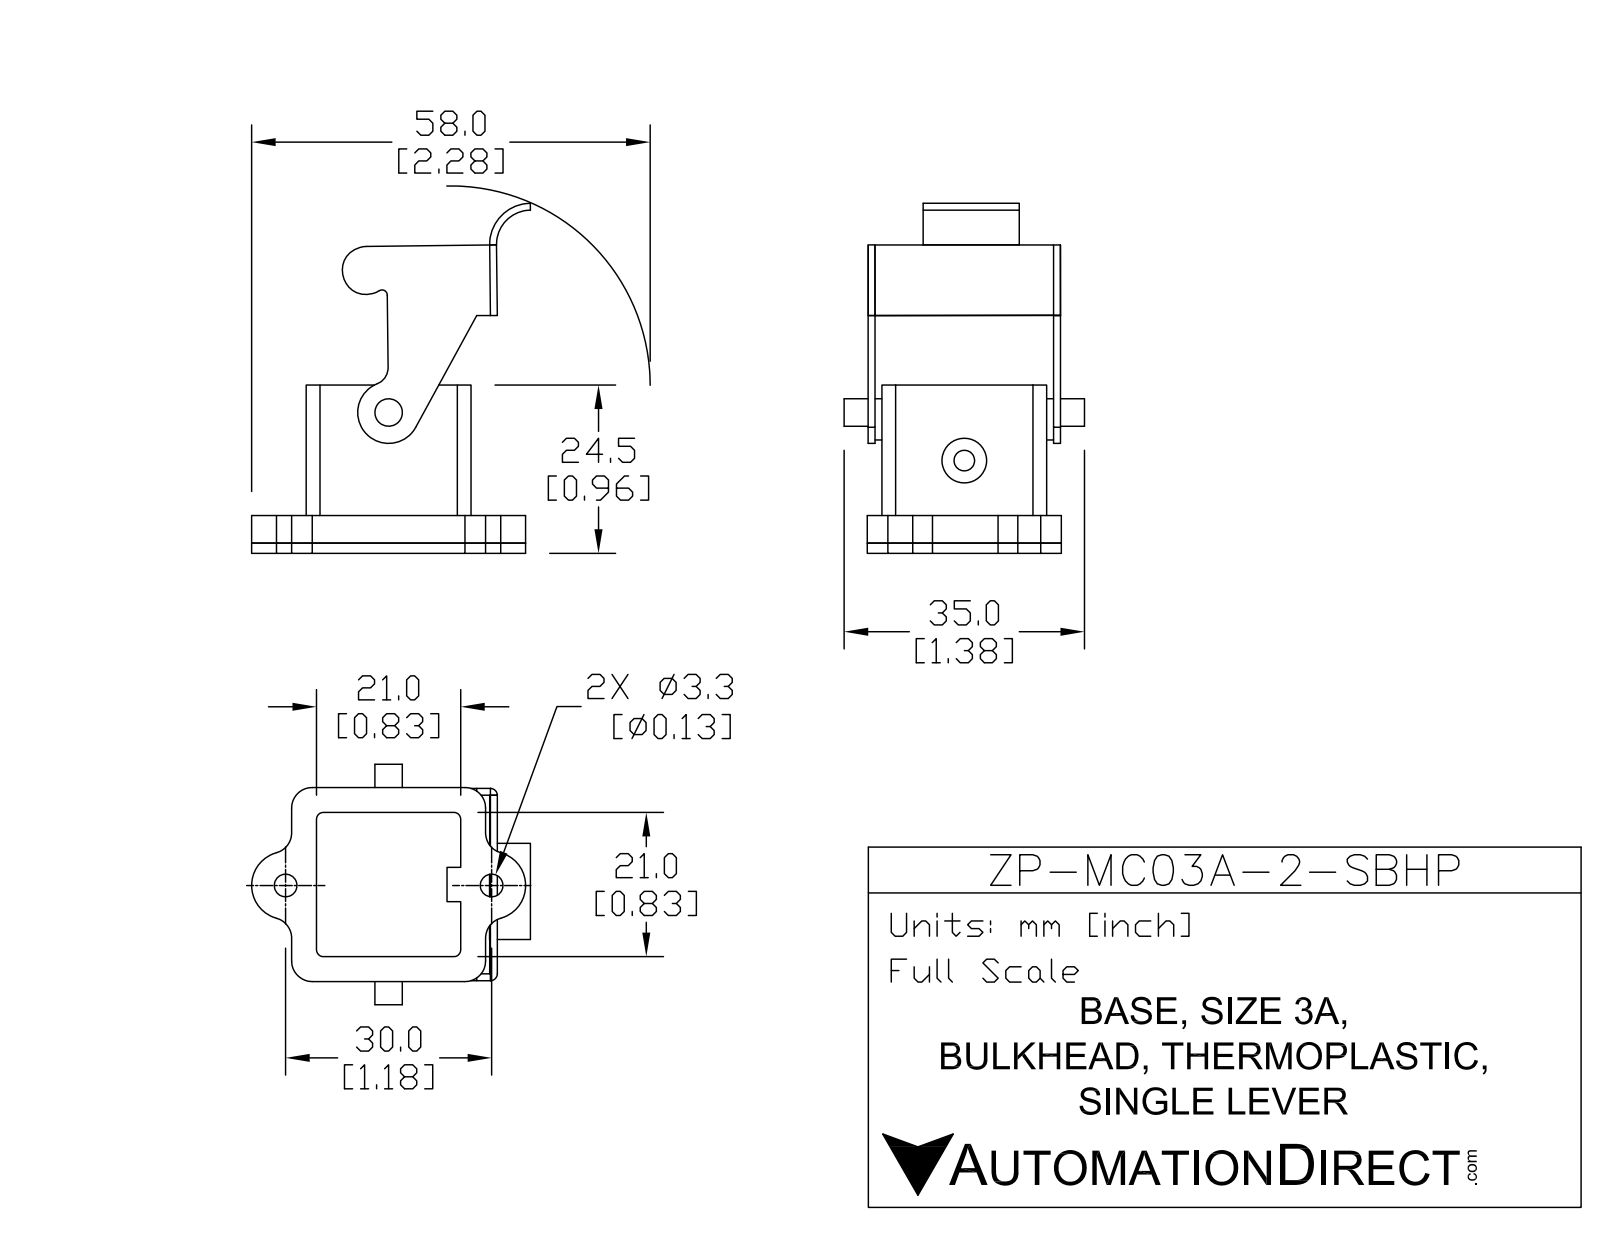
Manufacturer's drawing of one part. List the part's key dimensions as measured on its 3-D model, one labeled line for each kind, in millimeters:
Part name (STEP PRODUCT): ZP-MC03A-2-SBHP
STEP written by: SolidWorks 2011 (AUTOMOTIVE_DESIGN)
Units: millimetres
Bodies: 2 solids, 118 faces (53 planar, 62 cylindrical, 3 other)
Overall size (bounding box): 58.14 × 39.9 × 35
Volume: 8 140 mm³ · Surface area: 9 338 mm²
Round holes (diameter × count): ⌀3.3 ×2, ⌀3 ×1
Round bosses / shafts (diameter × count): ⌀6 ×2, ⌀4 ×2
Partial cylindrical surfaces — rounded edges, fillets, slot ends (radius × count): R2 ×10, R3 ×8, R1 ×4, R4.95 ×2, R0.5 ×1, R1 ×1, R3.45 ×1, R3.73 ×1
Main face-to-face distances: 2.56, 1.5, 22.49, 1.51, 24, 3.56, 27.56, 28.56, 1, 25
Hole centre spacings: 29.99
